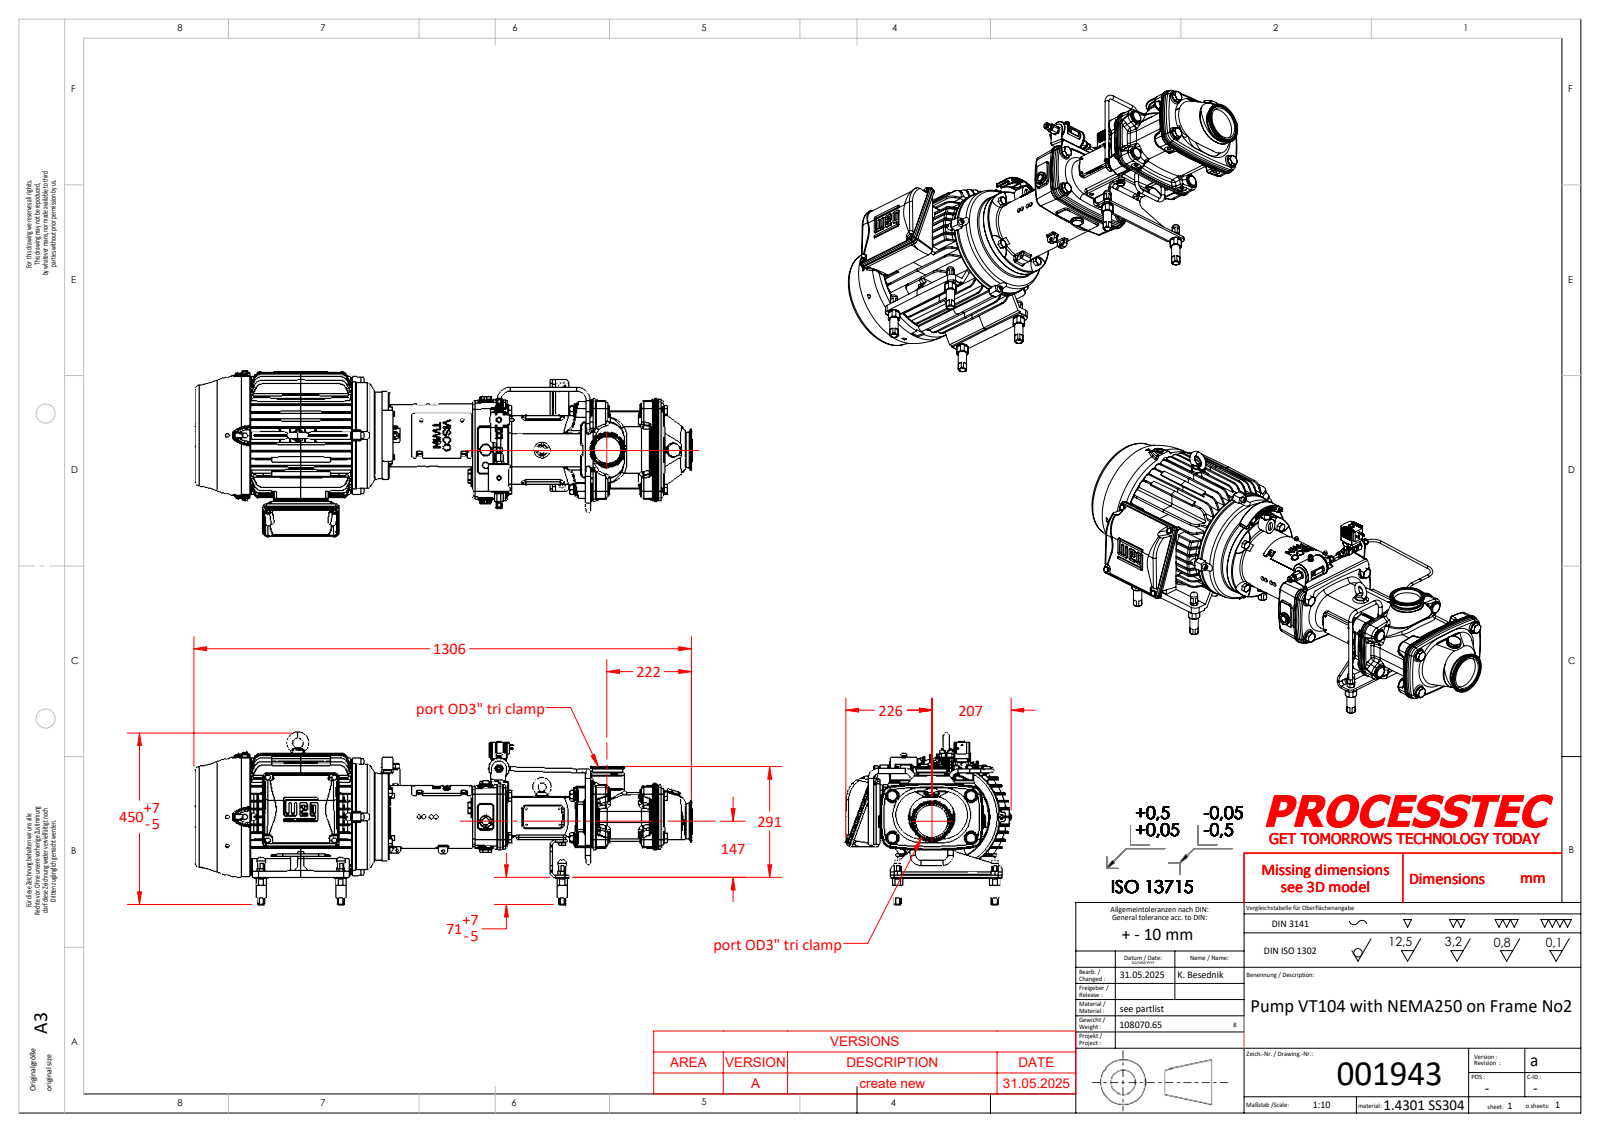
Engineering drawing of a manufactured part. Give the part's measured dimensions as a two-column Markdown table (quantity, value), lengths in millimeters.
| quantity | value |
| --- | --- |
| part name | 001076; 001086_DIN 6912 - M16 X 35 - A2-70; 001383; 001406 (+8 more) |
| STEP written by | SolidWorks 2023 (AUTOMOTIVE_DESIGN) |
| units | millimeters |
| bodies | 96 solids, 8583 faces (2999 planar, 2280 cylindrical, 3304 other) |
| overall size | 1305.99 × 449.75 × 434.2 |
| volume | 52 120 000 mm³ |
| surface area | 3 321 000 mm² |
| round holes (diameter × count) | 8 × 15, 8.5 × 8, 6 × 7, 5.9 × 6, 7.2 × 6, 10.2 × 6, 12 × 6, 14.5 × 6, 22.2 × 6, 4.35 × 5, 5 × 5, 7.5 × 5 |
| round bosses / shafts (diameter × count) | 30 × 10, 10 × 9, 8 × 9, 24 × 8, 22 × 7, 11.6 × 7, 19 × 6, 7 × 6 |
| partial cylindrical surfaces (radius × count) | 3 × 191, 5 × 62, 2 × 60, 1.5 × 48, 8 × 34, 6 × 30, 1.2 × 27, 4 × 21 |
| main face-to-face distances | 19.8, 39.6, 265.9, 14, 5.8, 121.2, 141, 101.4, 391.35, 657.25 |
| hole center spacings | 55, 108, 130.23, 107.22, 118.86, 41.49, 95.26, 110 |
